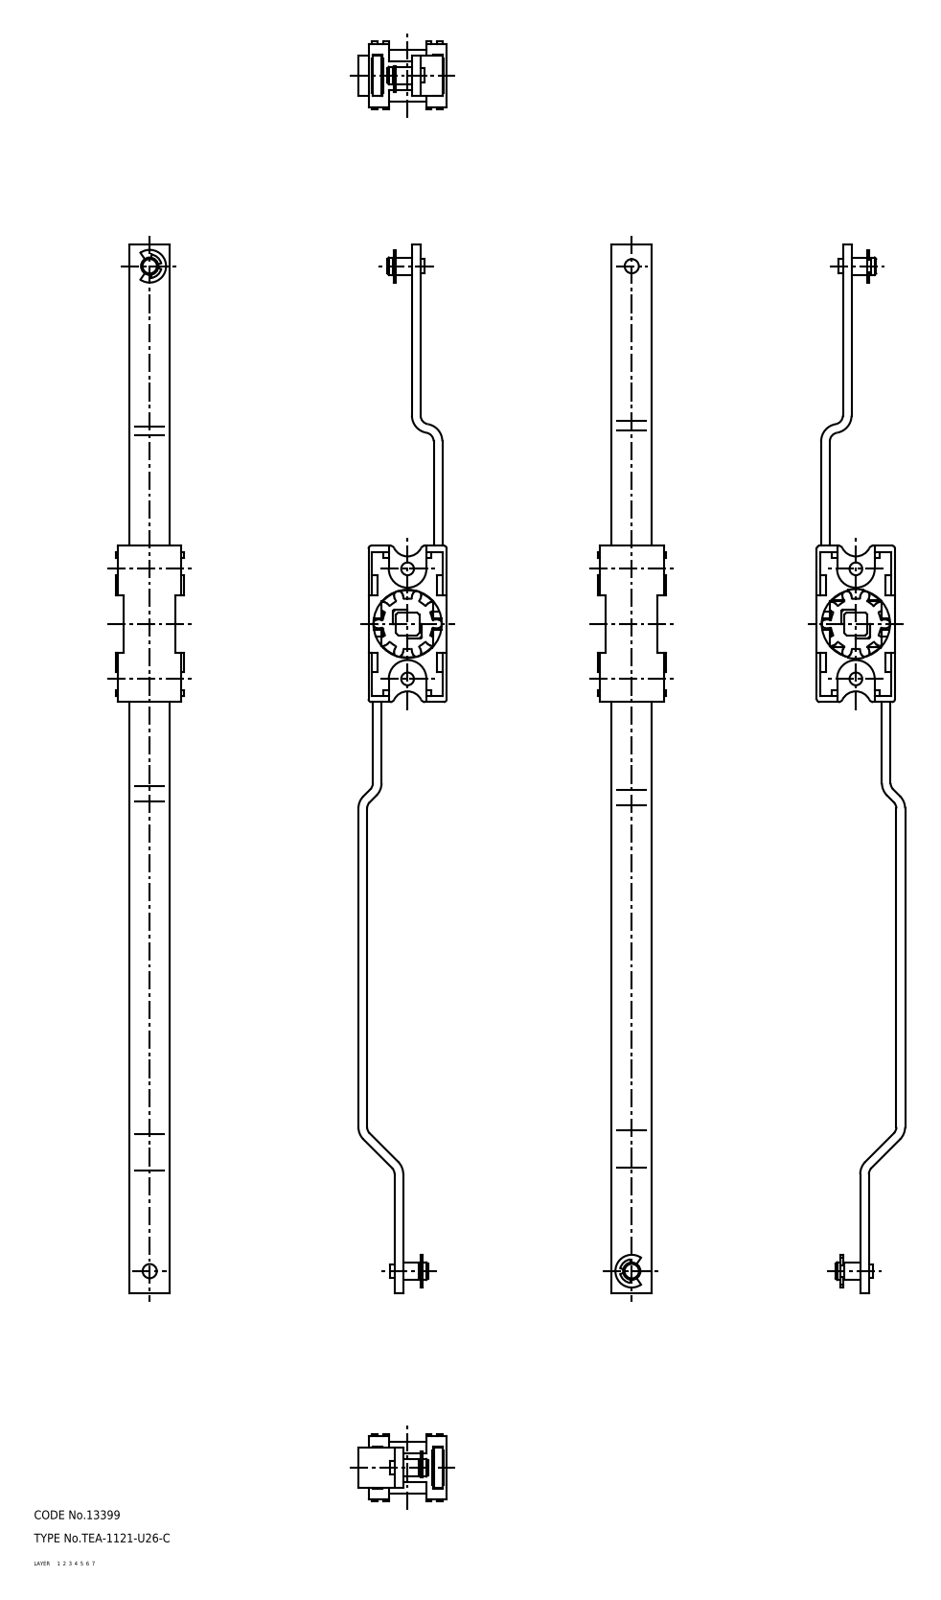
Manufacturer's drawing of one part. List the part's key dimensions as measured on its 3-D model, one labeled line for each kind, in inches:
Part name (STEP PRODUCT): rod_2; rod_1; TEA_1121_U26_C_8124_36
STEP written by: CADfix (AUTOMOTIVE_DESIGN)
Units: inches
Bodies: 3 solids, 644 faces (0 planar, 0 cylindrical, 644 other)
Overall size (bounding box): 14.252 × 1.201 × 0.921
Volume: 1.844 in³ · Surface area: 40.8 in²
